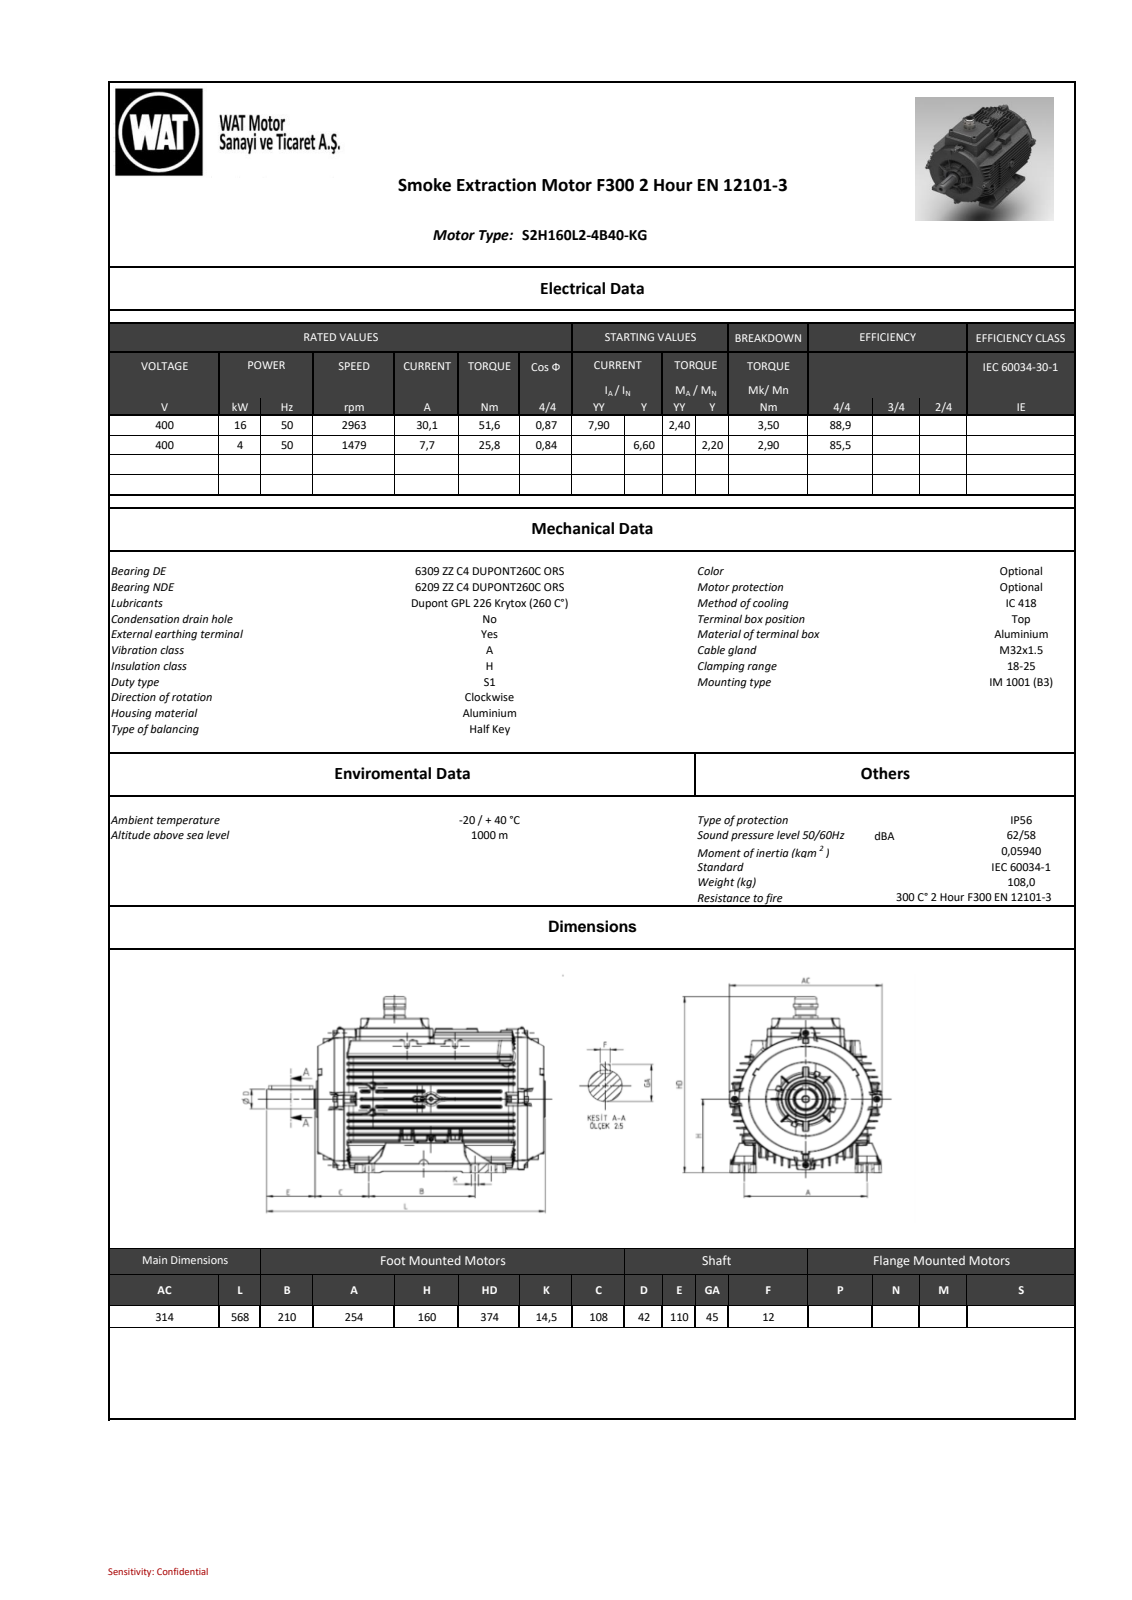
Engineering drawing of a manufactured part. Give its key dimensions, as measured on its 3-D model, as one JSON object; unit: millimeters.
{"part_name": "26036A749124f28o", "step_written_by": "SIEMENS PLM Software NX 11.0 (AP203_CONFIGURATION_CONTROLLED_3D_DESIGN_OF_MECHANICAL_PARTS_AND_ASSEMBLIES_MIM_LF)", "units": "millimeters", "bodies": {"solids": 0, "faces": 8861, "planar": 2015, "cylindrical": 3118, "other": 3728}, "overall_size": [568.5, 373.95, 314], "round_holes": [[4.6, 4], [10.2, 1], [13, 1], [18, 1], [54, 1], [68.67, 1]], "round_bosses_or_shafts": [[14.8, 4], [13, 4], [10, 4], [272.5, 1], [72, 1], [45, 1], [42, 1], [41.4, 1]], "partial_cylinders_radius": [[0.5, 773], [1, 752], [1.5, 224], [4, 109], [5, 76], [2.5, 50], [3, 13], [5.5, 8]], "face_to_face_distances": [11.85, 165.47, 144, 168, 9.32, 2.53, 156.15, 11.92, 21.47, 155.85]}
